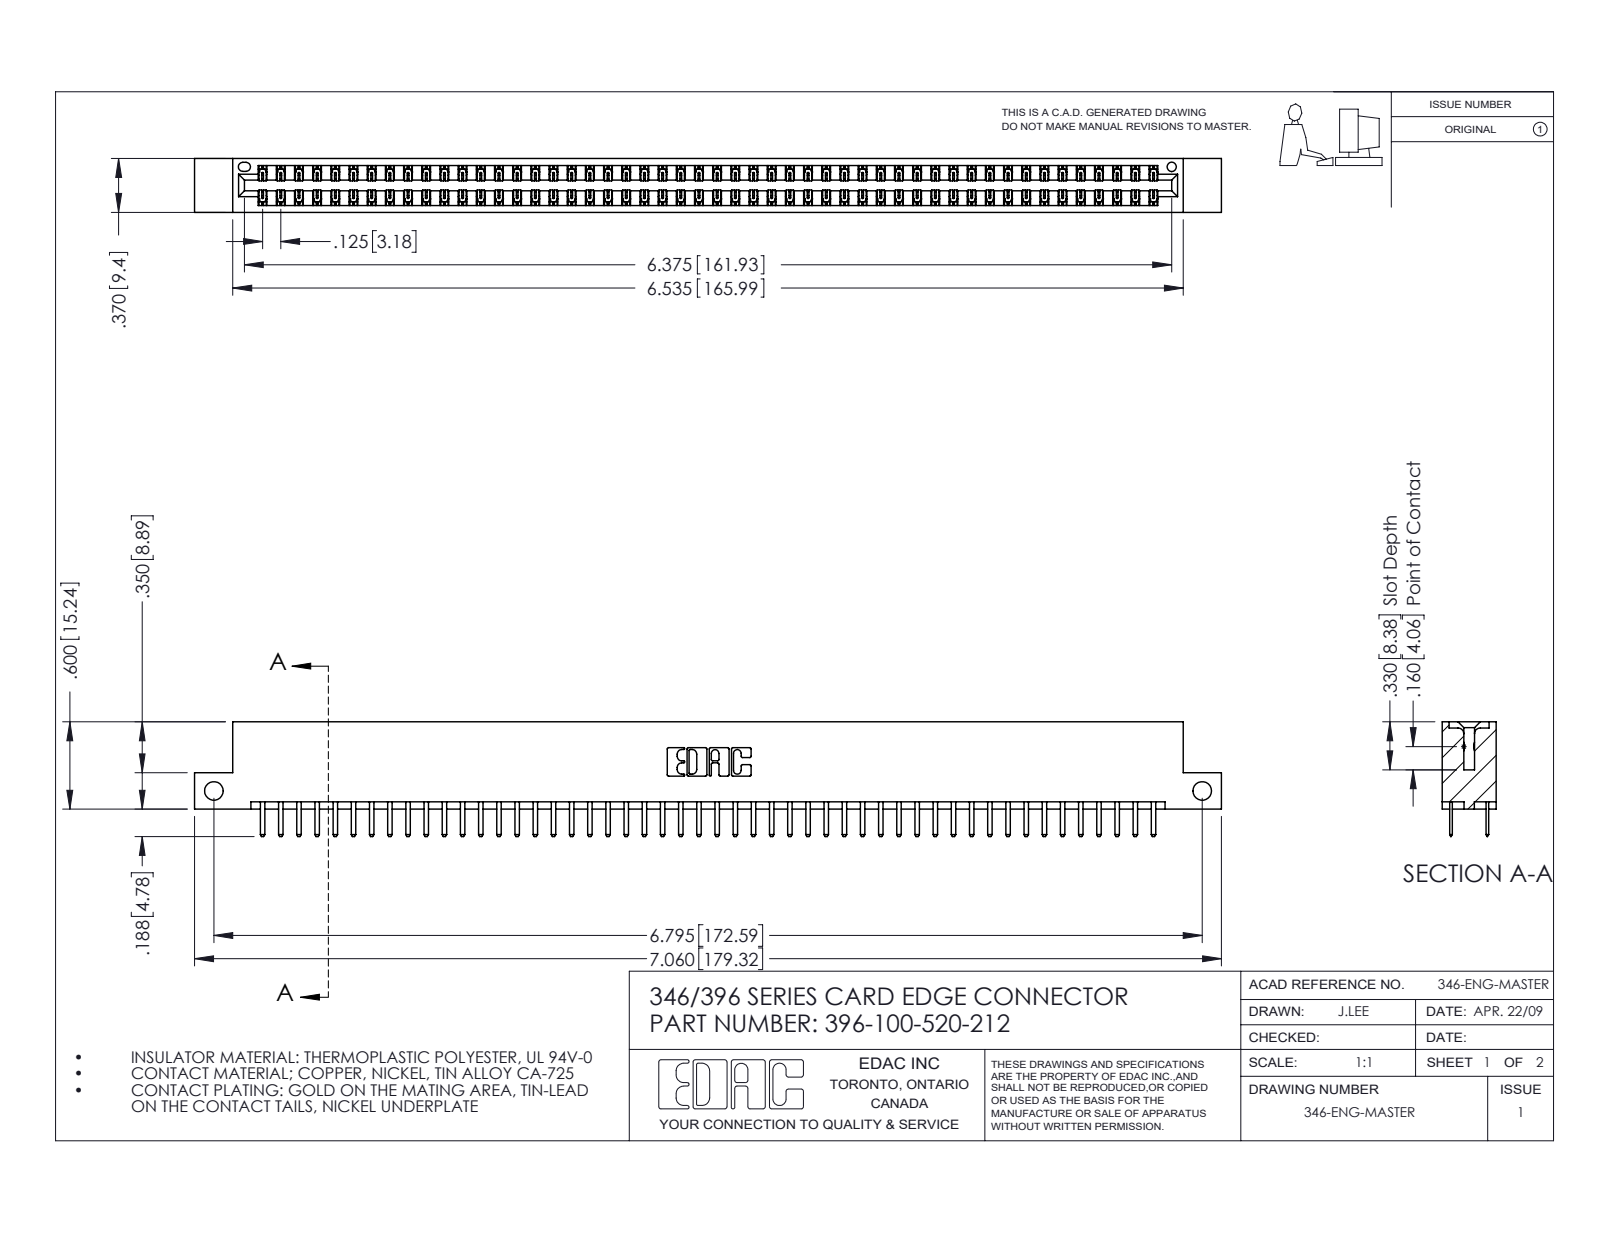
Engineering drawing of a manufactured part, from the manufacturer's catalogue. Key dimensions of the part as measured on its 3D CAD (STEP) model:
Part name (STEP PRODUCT): 346 Part_Flush Mounting Lugs - Side Mount; 396-100-520-212; 345-292-001_345-293-120
STEP written by: SolidWorks 2016 (CONFIG_CONTROL_DESIGN)
Units: inches
Bodies: 101 solids, 5722 faces (3776 planar, 1946 cylindrical, 0 other)
Overall size (bounding box): 7.06 × 0.788 × 0.37
Volume: 1.063 in³ · Surface area: 36.93 in²
Round holes (diameter × count): ⌀0.128 ×2, ⌀0.064 ×1
Partial cylindrical surfaces — rounded edges, fillets, slot ends (radius × count): R0.006 ×150, R0.01 ×104, R0.01 ×22, R0.007 ×6, R0.031 ×6, R0.026 ×3, R0.014 ×2, R0.022 ×2
Main face-to-face distances: 0.048, 0.322, 0.25, 0.37, 0.275, 0.072, 0.298, 0.025, 0.148, 0.222
Hole centre spacings: 6.795
